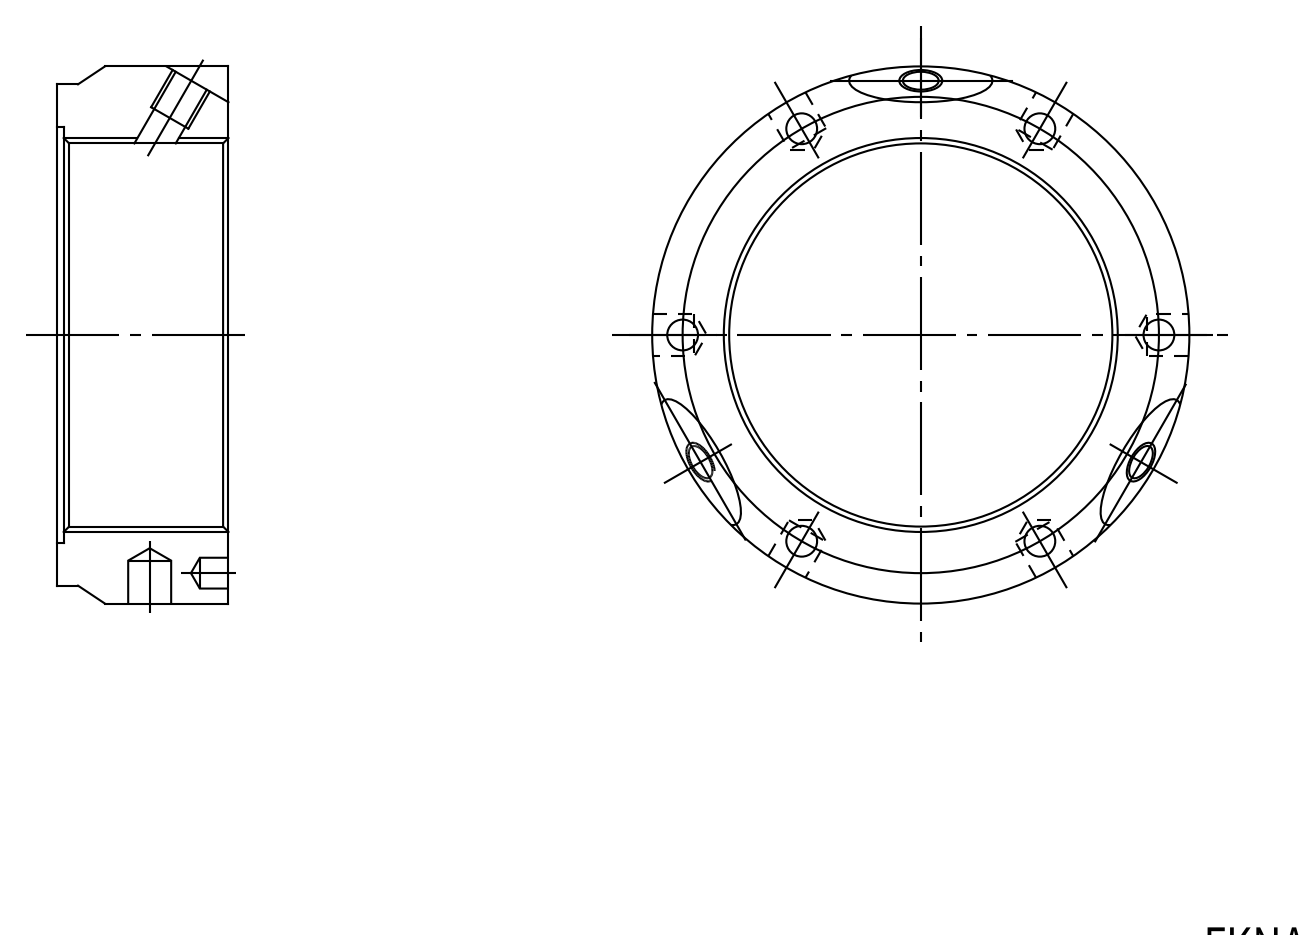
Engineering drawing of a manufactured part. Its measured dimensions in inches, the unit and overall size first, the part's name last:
Units: inches
Overall size (bounding box): 2.953 × 2.953 × 0.945
Round holes (diameter × count): ⌀0.169 ×6, ⌀0.236 ×3, ⌀0.24 ×3, ⌀0.194 ×2, ⌀0.194 ×1, ⌀2.165 ×1, ⌀2.283 ×1
Round bosses / shafts (diameter × count): ⌀2.953 ×1, ⌀2.756 ×1
Partial cylindrical surfaces — rounded edges, fillets, slot ends (radius × count): R0.787 ×3
Main face-to-face distances: 0.945, 0.059, 0.886
Hole centre spacings: 1.309, 1.309, 2.268, 2.619, 2.618
Volume: 2.755 in³ · Surface area: 23.3 in²
Bodies: 1 solid, 44 faces (6 planar, 25 cylindrical, 13 other)
Part name (STEP PRODUCT): FKD FKNA55
STEP written by: Autodesk Inventor LT (CONFIG_CONTROL_DESIGN)
